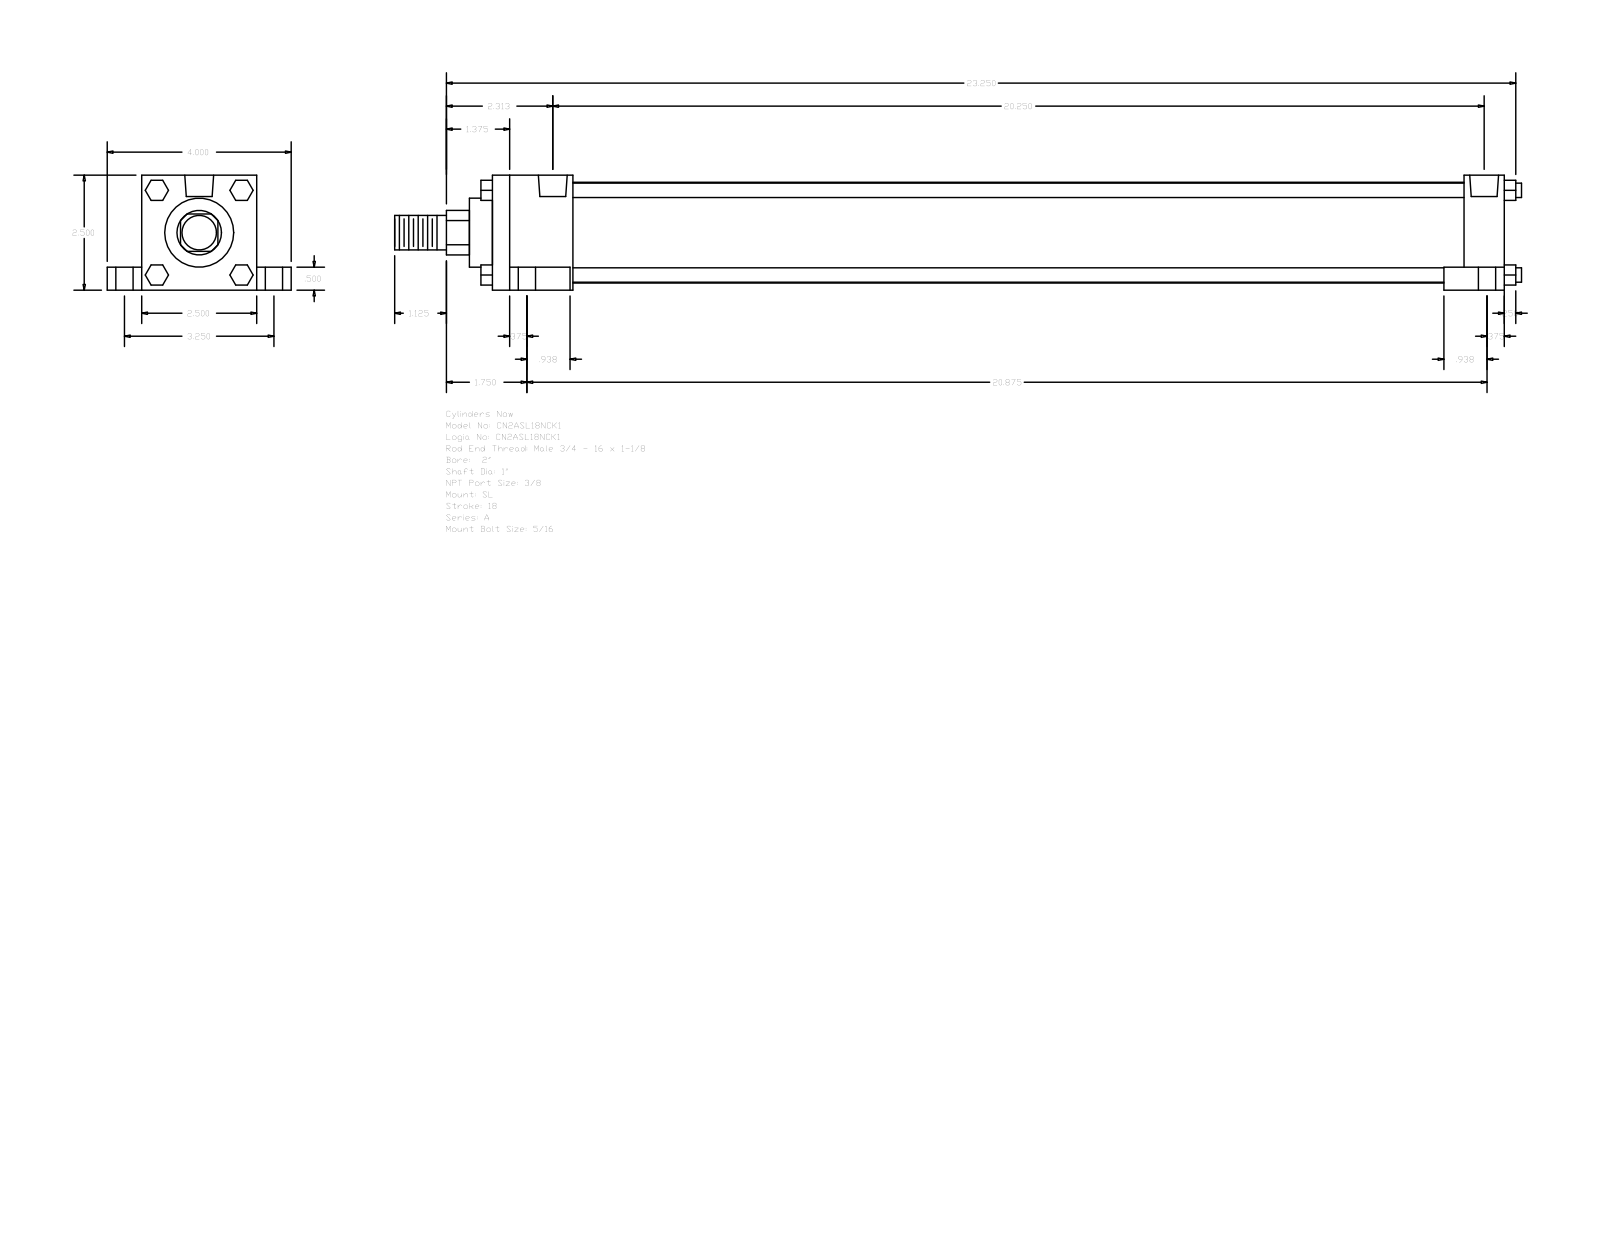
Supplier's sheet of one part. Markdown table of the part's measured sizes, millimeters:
| quantity | value |
| --- | --- |
| part name | A_SL__0200_1 |
| STEP written by | GSSL Pune (CONFIG_CONTROL_DESIGN) |
| units | millimeters |
| bodies | 0 solids, 148 faces (112 planar, 36 cylindrical, 0 other) |
| overall size | 622.3 × 101.6 × 63.5 |
| round holes (diameter × count) | 5.56 × 4, 9.53 × 4, 15.88 × 4, 15.93 × 2 |
| round bosses / shafts (diameter × count) | 7.94 × 4, 55.63 × 1, 38.1 × 1, 25.4 × 1, 19.05 × 1 |
| partial cylindrical surfaces (radius × count) | 12.29 × 1 |
| main face-to-face distances | 63.5, 12.7, 558.8, 50.8, 22.22, 19.05, 82.55, 44.45, 514.35, 536.58 |
| hole center spacings | 41.3, 41.64, 43.67, 44.22, 82.54, 508.78, 515.99, 517.58 |
